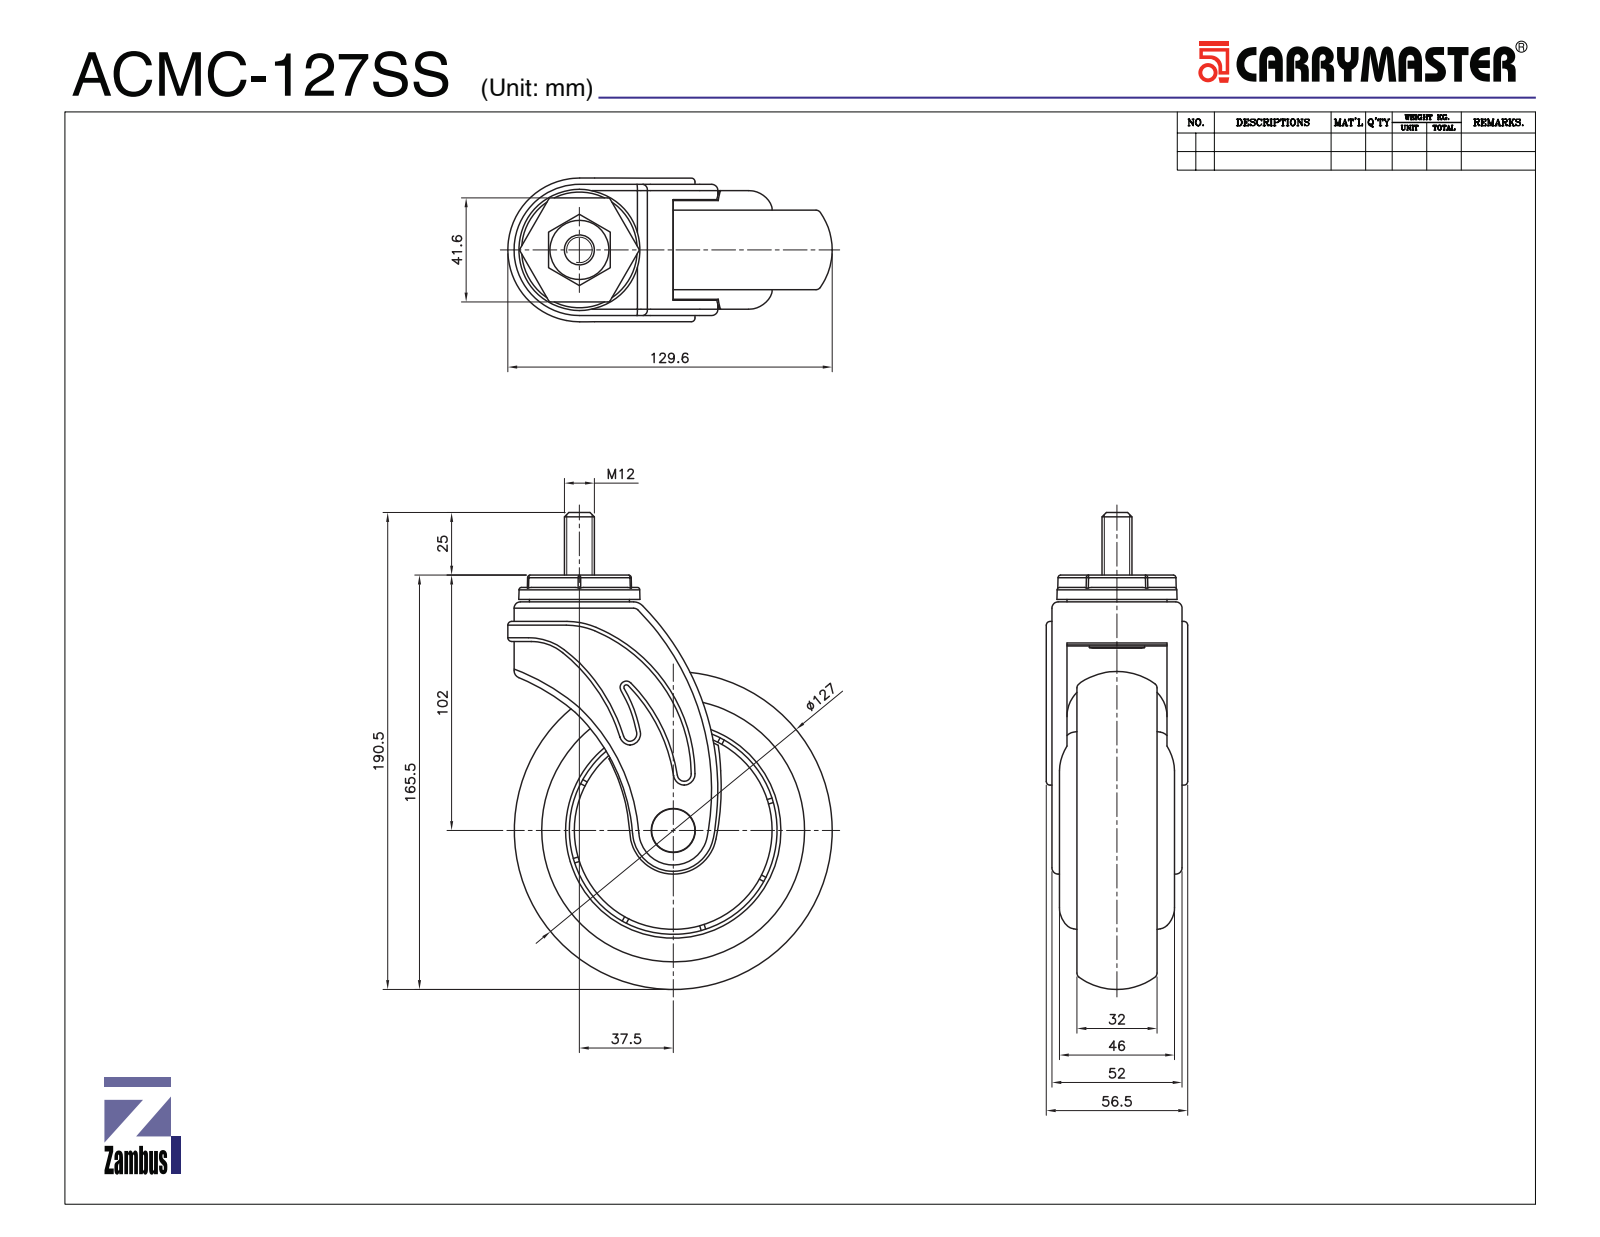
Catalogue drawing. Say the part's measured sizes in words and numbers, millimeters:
The part is named "ACMC-127SS; ACMC-127 S TOP PLATE; ACMC-127 TOP PLATE COVER; ACMC-127 NON BRAKE FRAME (+1 more)". Its 3-D file was written by "SolidWorks 2019 (CONFIG_CONTROL_DESIGN)". It is 4 solids with 277 faces: 65 planar, 123 cylindrical and 89 other. Overall it measures 190.5 by 129.4 by 57.1 millimeters. Its volume is 544 921 cubic millimeters and its surface area 81 535 square millimeters. Round holes: 1 of diameter 17.3, 1 of diameter 37, 1 of diameter 83, 1 of diameter 105.01. Round bosses or shafts: 1 of diameter 105, 1 of diameter 79, 1 of diameter 78.59, 1 of diameter 40, 1 of diameter 25, 1 of diameter 22, 1 of diameter 17, 1 of diameter 10.25. Partial cylindrical surfaces (rounded edges, fillets, slot ends): 13 of radius 1, 4 of radius 4.5, 2 of radius 2.5, 1 of radius 5, 1 of radius 16.3, 1 of radius 16.8, 1 of radius 20, 1 of radius 20.25. The main face-to-face distances are 4.25, 36.25, 32, 6, 10.25, 42.25, 46.5, 40.5, 4, 6.25.
